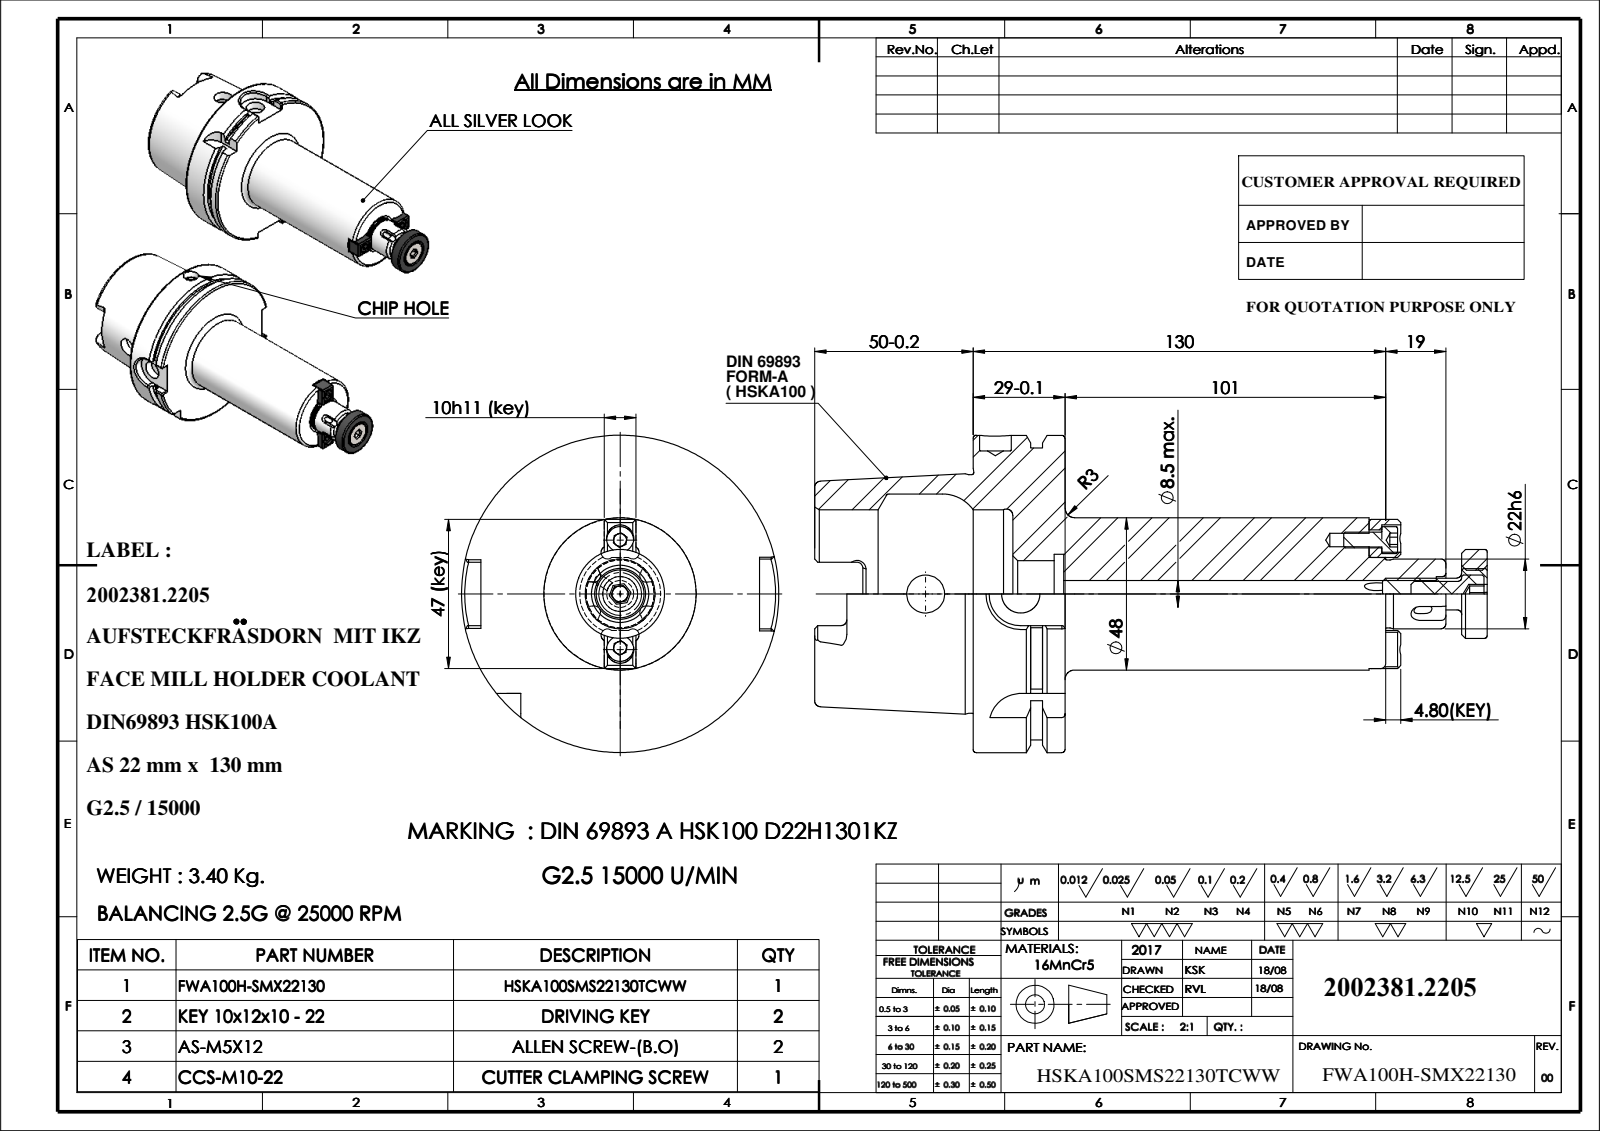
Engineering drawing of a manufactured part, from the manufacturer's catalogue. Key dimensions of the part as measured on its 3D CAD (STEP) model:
Part name (STEP PRODUCT): CCS-M10-22-1 LONG; CCS-M10-22-2; 91100A-AS522130; HSKA100SMS22130TCWW (+5 more)
STEP written by: SolidWorks 2009 (CONFIG_CONTROL_DESIGN)
Units: millimetres
Bodies: 8 solids, 429 faces (181 planar, 106 cylindrical, 142 other)
Overall size (bounding box): 212 × 100 × 100
Volume: 444 956 mm³ · Surface area: 77 234 mm²
Round holes (diameter × count): ⌀3 ×4, ⌀4.2 ×2, ⌀5.4 ×2, ⌀8.6 ×2, ⌀12 ×2, ⌀8.5 ×1, ⌀10 ×1, ⌀11 ×1, ⌀15 ×1, ⌀21 ×1, ⌀25 ×1, ⌀53 ×1
Round bosses / shafts (diameter × count): ⌀8.5 ×2, ⌀5 ×2, ⌀100 ×1, ⌀92 ×1, ⌀75.16 ×1, ⌀48 ×1, ⌀28 ×1, ⌀22 ×1
Partial cylindrical surfaces — rounded edges, fillets, slot ends (radius × count): R2 ×8, R1.8 ×6, R4.88 ×4, R10 ×2, R11 ×1
Main face-to-face distances: 28.95, 12.5, 16.45, 50, 62.5, 78.95, 180, 130, 117.5, 101.05
Hole centre spacings: 0.5, 17, 17.5, 34.5, 30, 34, 35
